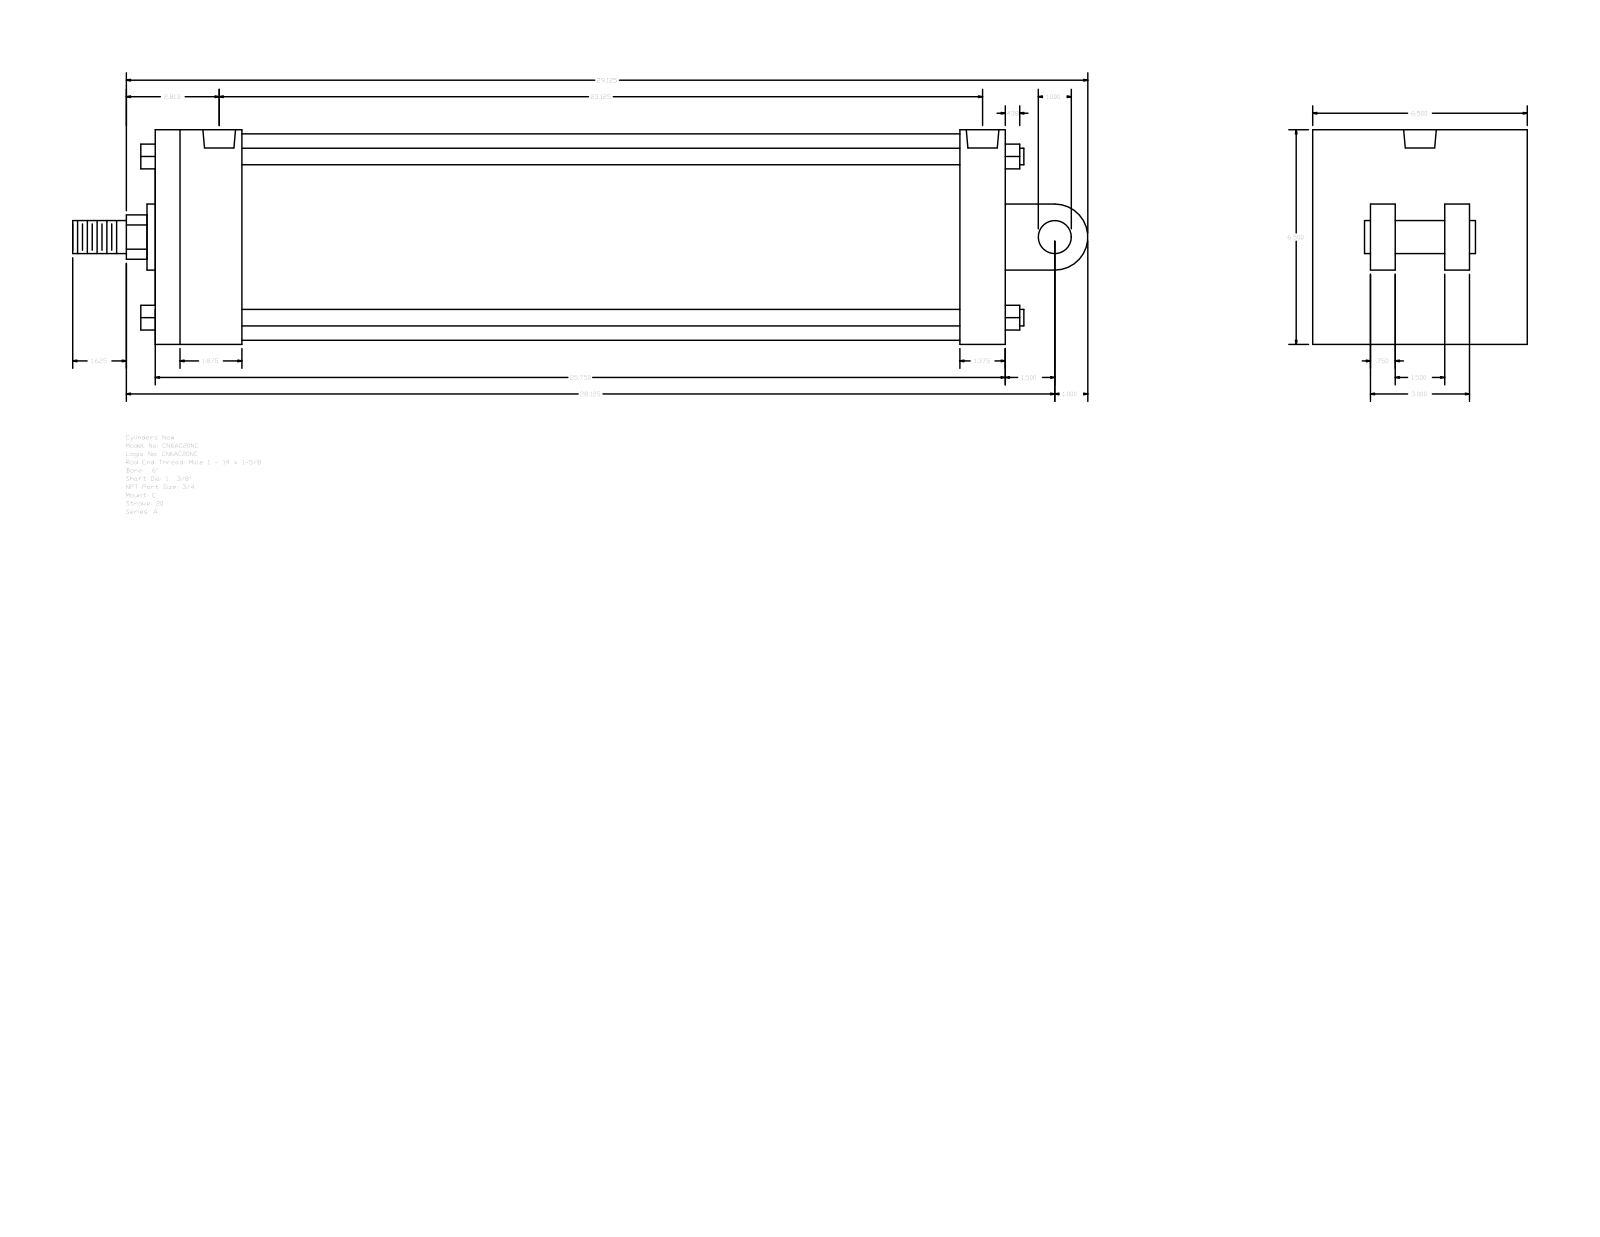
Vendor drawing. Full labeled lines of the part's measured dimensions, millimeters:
Part name (STEP PRODUCT): A_C__0600_1.375
STEP written by: GSSL Pune (CONFIG_CONTROL_DESIGN)
Units: millimetres
Bodies: 0 solids, 135 faces (102 planar, 33 cylindrical, 0 other)
Overall size (bounding box): 781.05 × 165.1 × 165.1
Round holes (diameter × count): ⌀15.08 ×4, ⌀25.12 ×2
Round bosses / shafts (diameter × count): ⌀12.7 ×4, ⌀25.4 ×2, ⌀158.75 ×1, ⌀50.8 ×1, ⌀34.92 ×1
Partial cylindrical surfaces — rounded edges, fillets, slot ends (radius × count): R17.06 ×1, R25.4 ×1
Main face-to-face distances: 165.1, 654.04, 57.15, 19.05, 66.67, 587.37, 619.12, 552.45, 34.92, 63.5
Hole centre spacings: 5.56, 576.25, 581.81, 587.37
